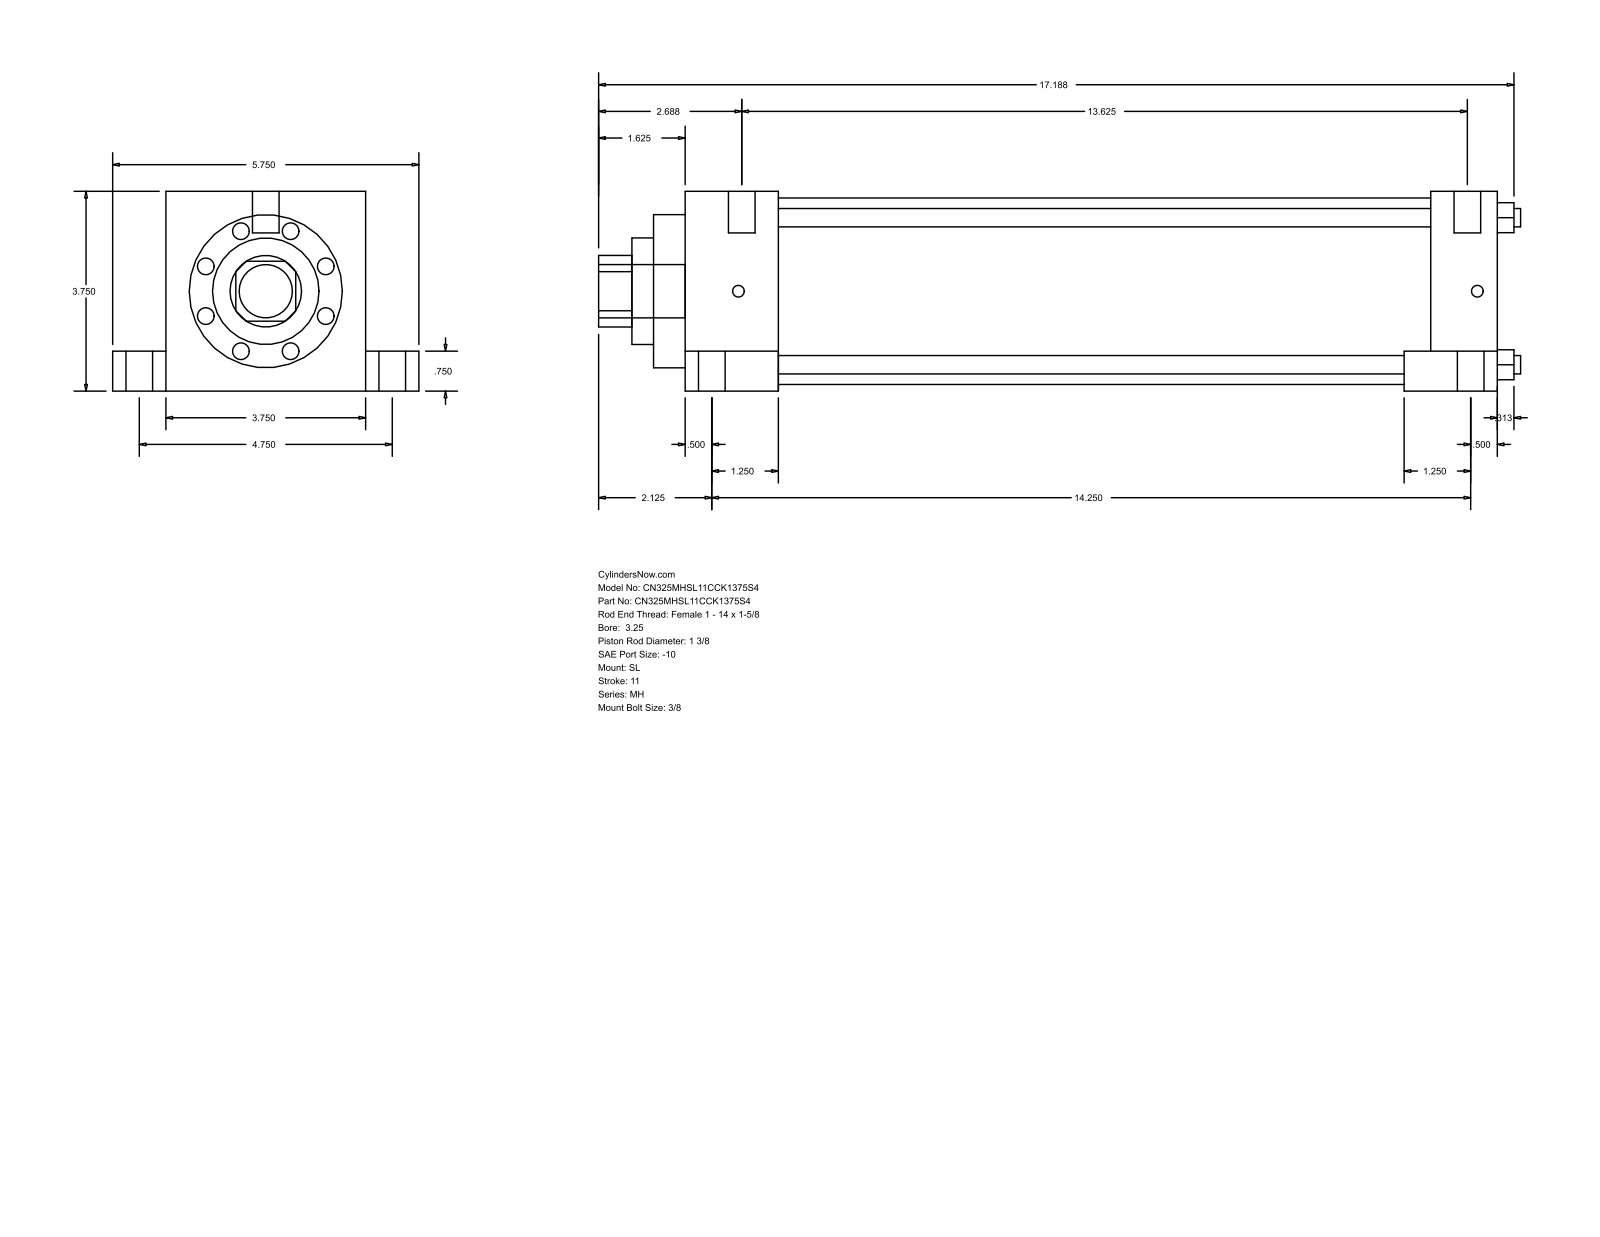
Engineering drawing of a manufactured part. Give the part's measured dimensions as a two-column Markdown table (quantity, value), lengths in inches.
| quantity | value |
| --- | --- |
| part name | MH_SL__0325_1.375 |
| STEP written by | GSSL Pune (CONFIG_CONTROL_DESIGN) |
| units | inches |
| bodies | 0 solids, 110 faces (77 planar, 33 cylindrical, 0 other) |
| overall size | 17.313 × 5.75 × 3.75 |
| round holes (diameter × count) | 0.345 × 4, 1.375 × 1, 2 × 1, 2.875 × 1, 3.5 × 1 |
| round bosses / shafts (diameter × count) | 0.5 × 6, 0.75 × 4, 0.219 × 4, 1 × 1 |
| partial cylindrical surfaces (radius × count) | 0.672 × 1 |
| main face-to-face distances | 3.75, 15.25, 1.75, 13.5, 1, 4.75, 0.75, 3, 14, 12.25 |
| hole center spacings | 1.952, 2.76, 3.903 |
